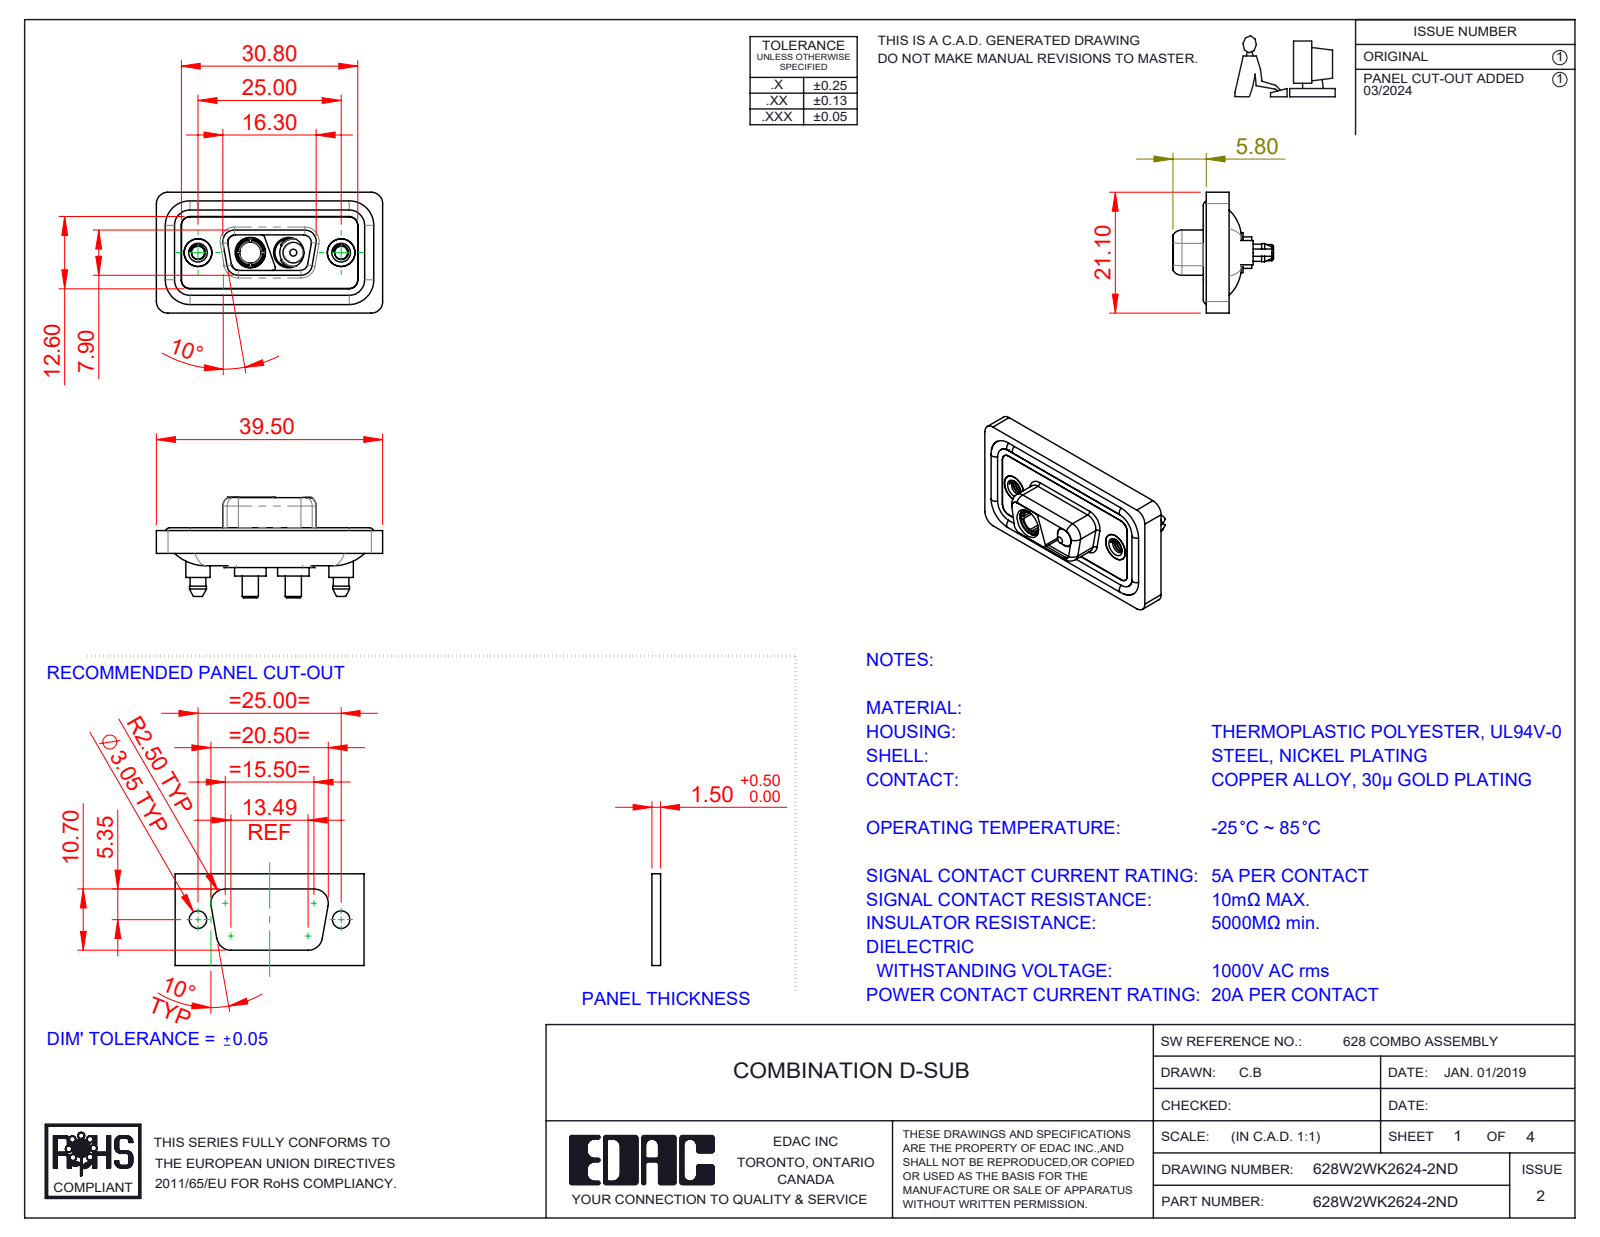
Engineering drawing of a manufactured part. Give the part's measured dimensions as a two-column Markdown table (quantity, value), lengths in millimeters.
| quantity | value |
| --- | --- |
| part name | 628Combo Threaded Boardlock_D; 628W2WK2624-2ND; 628Combo Waterproof Housing_09 Contacts; 628Combo Shell Rear_09 Contacts (+4 more) |
| STEP written by | SolidWorks 2023 (CONFIG_CONTROL_DESIGN) |
| units | millimeters |
| bodies | 11 solids, 566 faces (160 planar, 279 cylindrical, 127 other) |
| overall size | 39.5 × 21.1 × 17.55 |
| volume | 4 738 mm³ |
| surface area | 7 683 mm² |
| round holes (diameter × count) | 4.85 × 4, 2.26 × 2, 4 × 2, 4.05 × 2, 5 × 2, 5.3 × 2, 3.7 × 1 |
| round bosses / shafts (diameter × count) | 1.6 × 4, 5.5 × 2, 5.4 × 2, 5.2 × 2, 4.95 × 2, 4.8 × 2, 4.75 × 2, 4.25 × 2 |
| partial cylindrical surfaces (radius × count) | 1.5 × 24, 2 × 18, 1.6 × 10, 1.35 × 8, 0.5 × 6, 0.25 × 4, 0.6 × 4, 0.65 × 4 |
| main face-to-face distances | 0.4, 1.1, 2.9, 1.6, 0.5, 1.8, 5.65, 1.5, 4, 5.35 |
| hole center spacings | 9.14, 15.86, 6.72, 25 |
